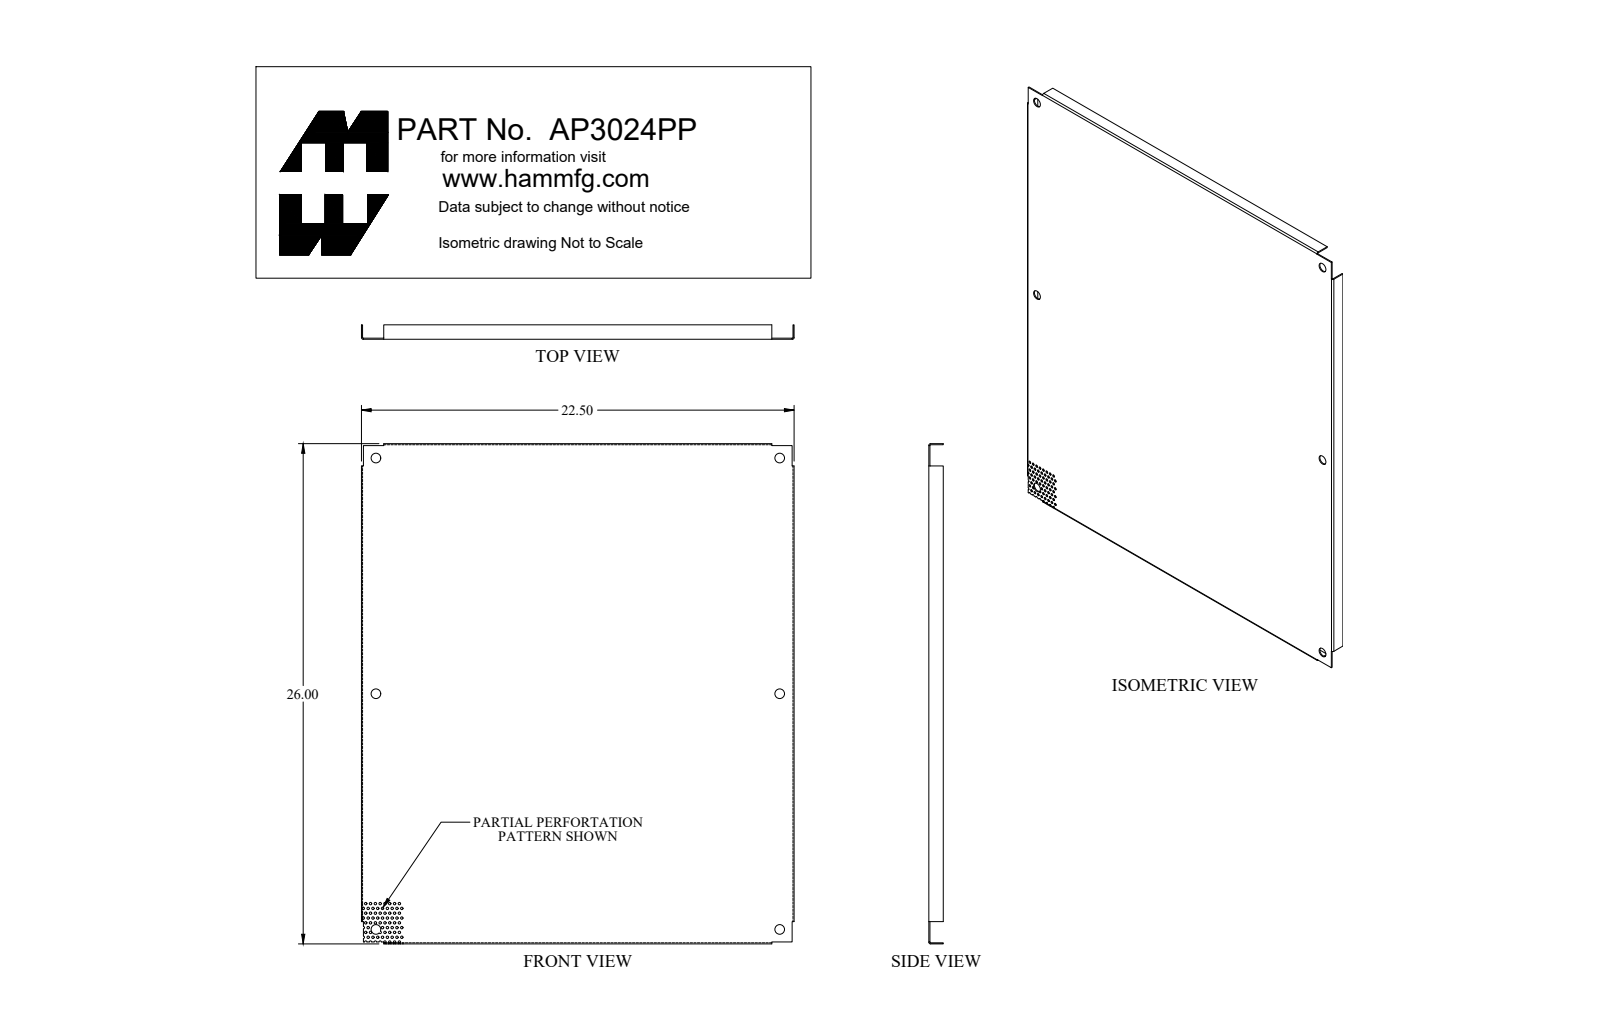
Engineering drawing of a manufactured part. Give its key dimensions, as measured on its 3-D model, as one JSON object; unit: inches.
{"part_name": "AP3024PP_Default", "step_written_by": "SolidWorks 2019 (CONFIG_CONTROL_DESIGN)", "units": "inches", "bodies": {"solids": 1, "faces": 264, "planar": 43, "cylindrical": 213, "other": 8}, "overall_size": [26, 22.5, 0.75], "volume_in3": 36.51, "surface_area_in2": 1289, "round_holes": [[0.125, 74], [0.5, 6], [0.125, 2]], "partial_cylinders_radius": [[0.063, 15], [0.062, 6], [0.029, 4], [0.086, 4]], "face_to_face_distances": [0.057, 22.443, 25.943, 22.386, 22.5, 26, 25.886, 0.75, 0.693, 0.102], "hole_center_spacings": [0.28, 0.5, 0.25, 0.559, 0.451, 0.76, 0.673, 0.75]}
